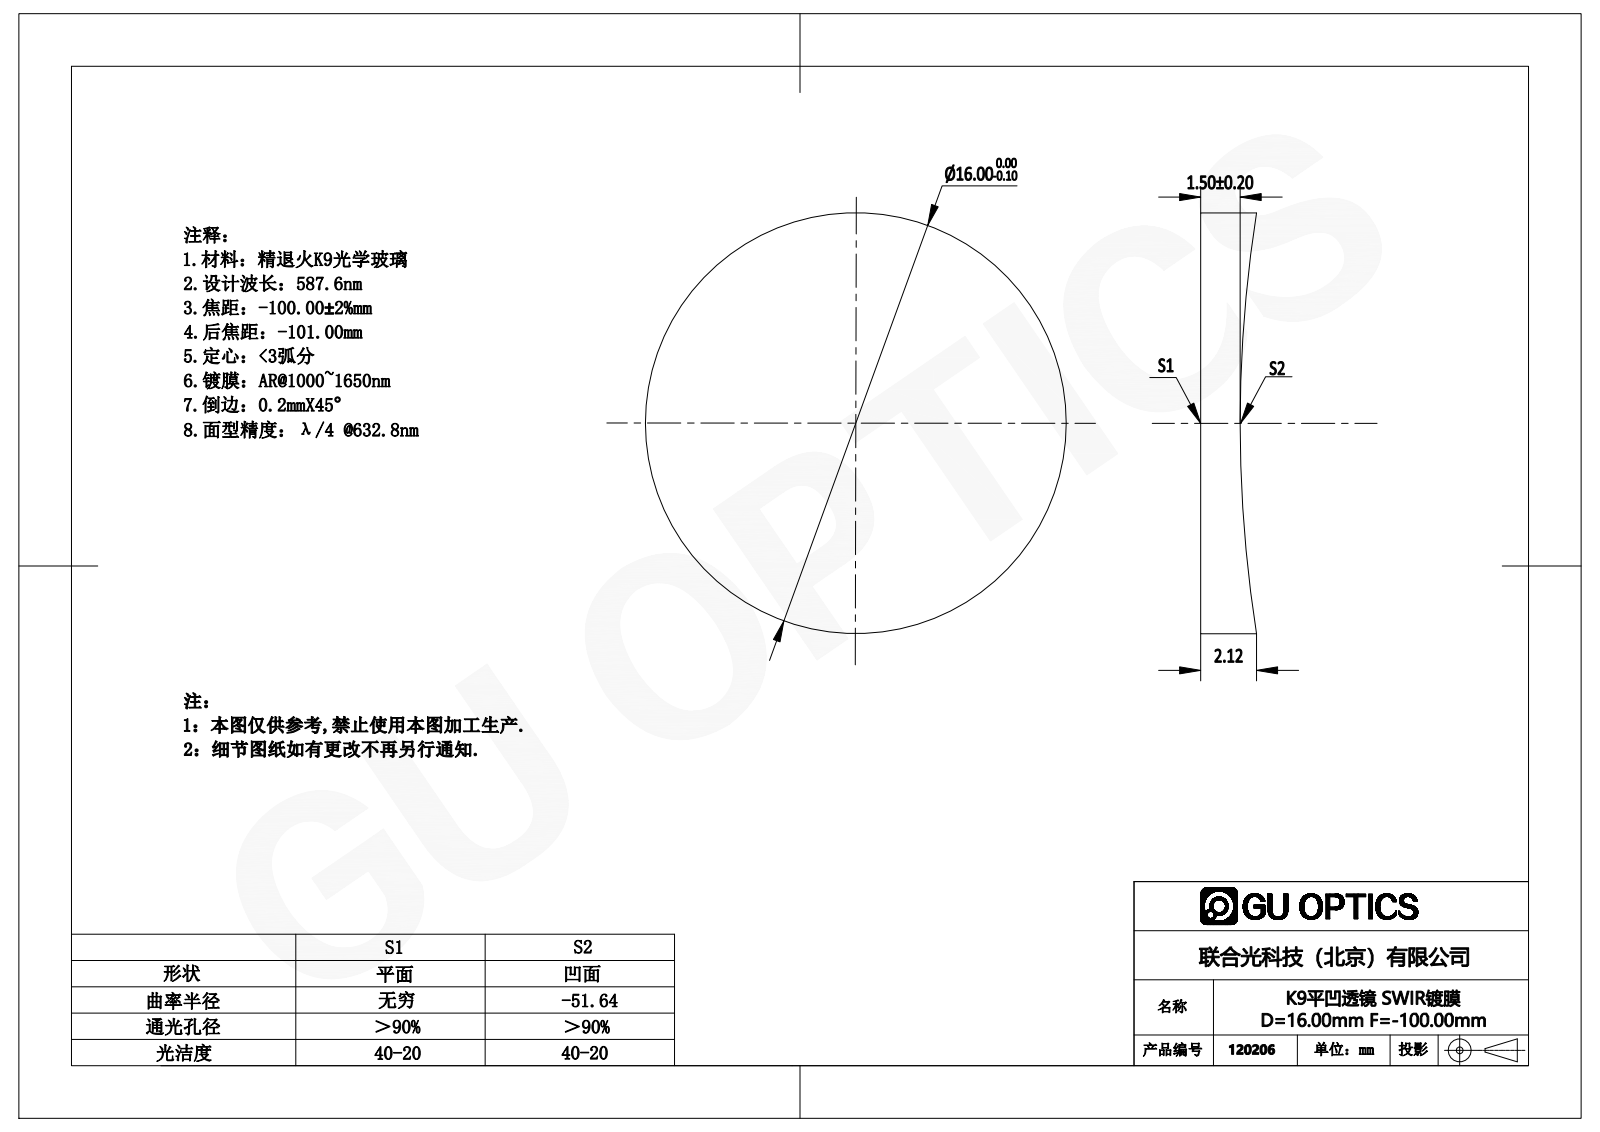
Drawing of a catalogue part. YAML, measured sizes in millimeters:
part_name: "120146"
step_written_by: "SolidWorks 2016 (AUTOMOTIVE_DESIGN)"
units: millimeters
bodies: {solids: 1, faces: 5, planar: 1, cylindrical: 2, other: 2}
overall_size: [16, 16, 2.12]
volume: 364
surface_area: 510
round_bosses_or_shafts:
  - {diameter: 16, count: 1}
